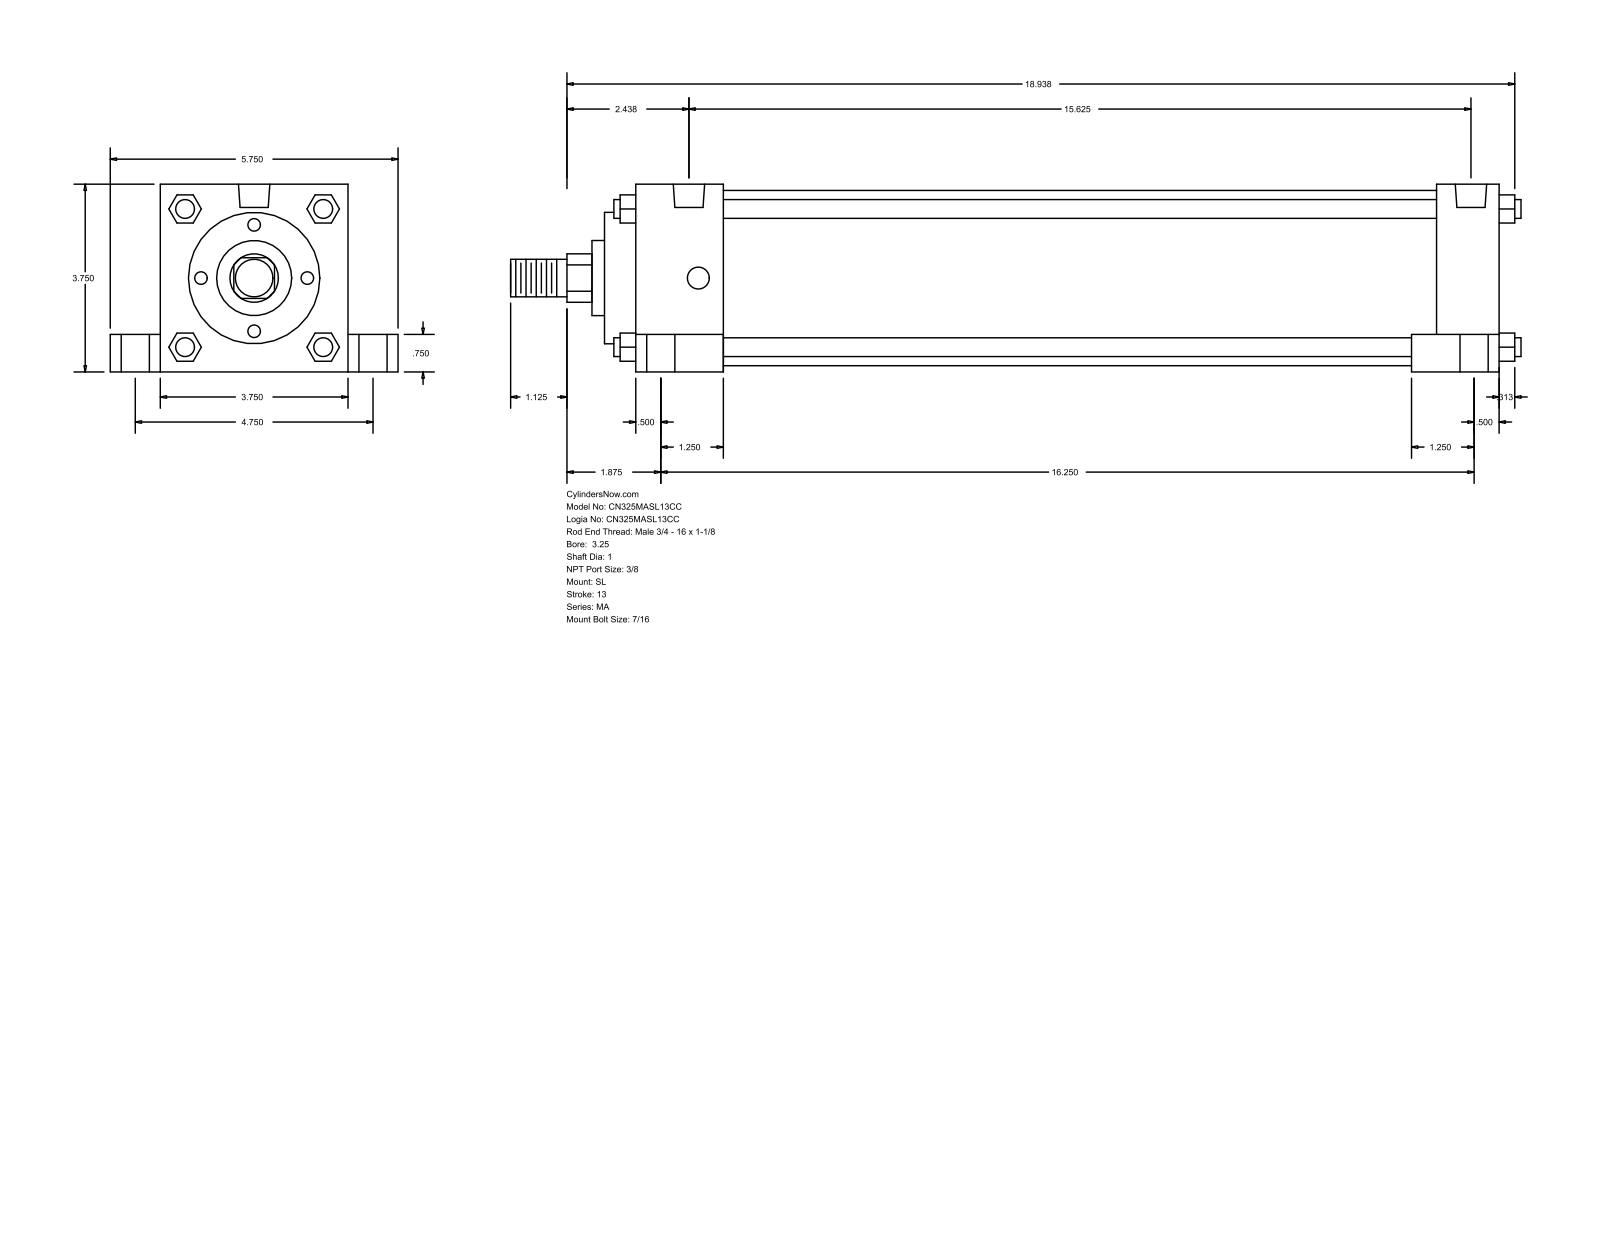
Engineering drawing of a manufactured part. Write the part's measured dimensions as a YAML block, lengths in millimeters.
part_name: "MA_SL__0325_1"
step_written_by: "GSSL Pune (CONFIG_CONTROL_DESIGN)"
units: millimeters
bodies: {solids: 0, faces: 150, planar: 113, cylindrical: 37, other: 0}
overall_size: [512.76, 146.05, 95.25]
round_holes:
  - {diameter: 11.11, count: 4}
  - {diameter: 14.29, count: 4}
  - {diameter: 20.64, count: 4}
  - {diameter: 15.93, count: 2}
round_bosses_or_shafts:
  - {diameter: 9.53, count: 4}
  - {diameter: 88.9, count: 1}
  - {diameter: 66.67, count: 1}
  - {diameter: 38.1, count: 1}
  - {diameter: 25.4, count: 1}
  - {diameter: 19.05, count: 1}
partial_cylinders:
  - {radius: 12.29, count: 1}
face_to_face_distances: [95.24, 438.15, 15.87, 25.41, 120.65, 454.02, 19.05, 406.4, 31.75, 44.46]
hole_center_spacings: [60.35, 60.66, 62, 63.27, 120.66, 387.35, 398.31, 403.01]
